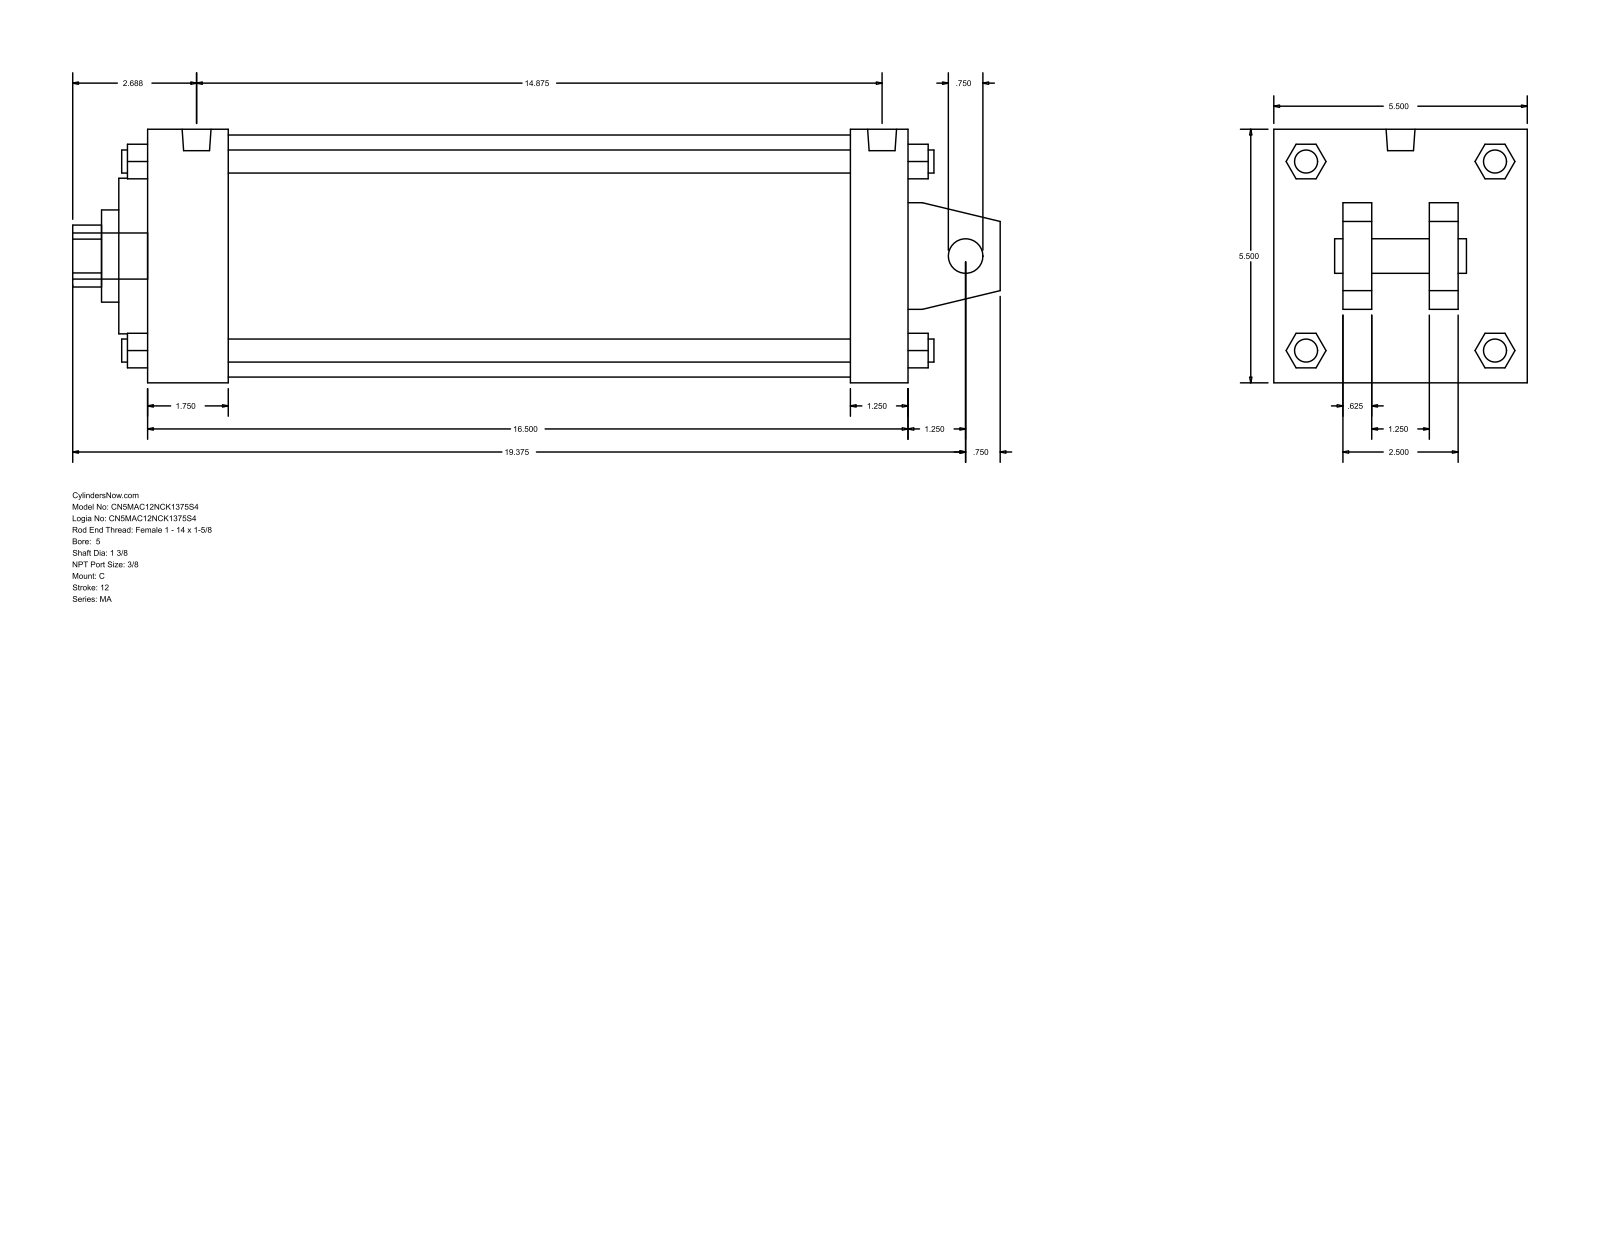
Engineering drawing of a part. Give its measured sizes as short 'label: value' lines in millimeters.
name: MA_C__0500_1.375
written by: GSSL Pune (CONFIG_CONTROL_DESIGN)
unit: mm
bodies: 0 solids, 141 faces (109 planar, 32 cylindrical, 0 other)
size: 511.18 × 139.7 × 139.7
holes: 1× ⌀19.05, 1× ⌀34.92, 1× ⌀50.8, 1× ⌀85.72, 1× ⌀133.35
bosses: 4× ⌀12.7, 4× ⌀11.11, 2× ⌀15.93, 1× ⌀25.4
rounds: 1× R17.06
face distances: 139.7, 419.11, 15.87, 31.76, 387.35, 44.45, 342.9, 374.66, 38.1, 101.6
